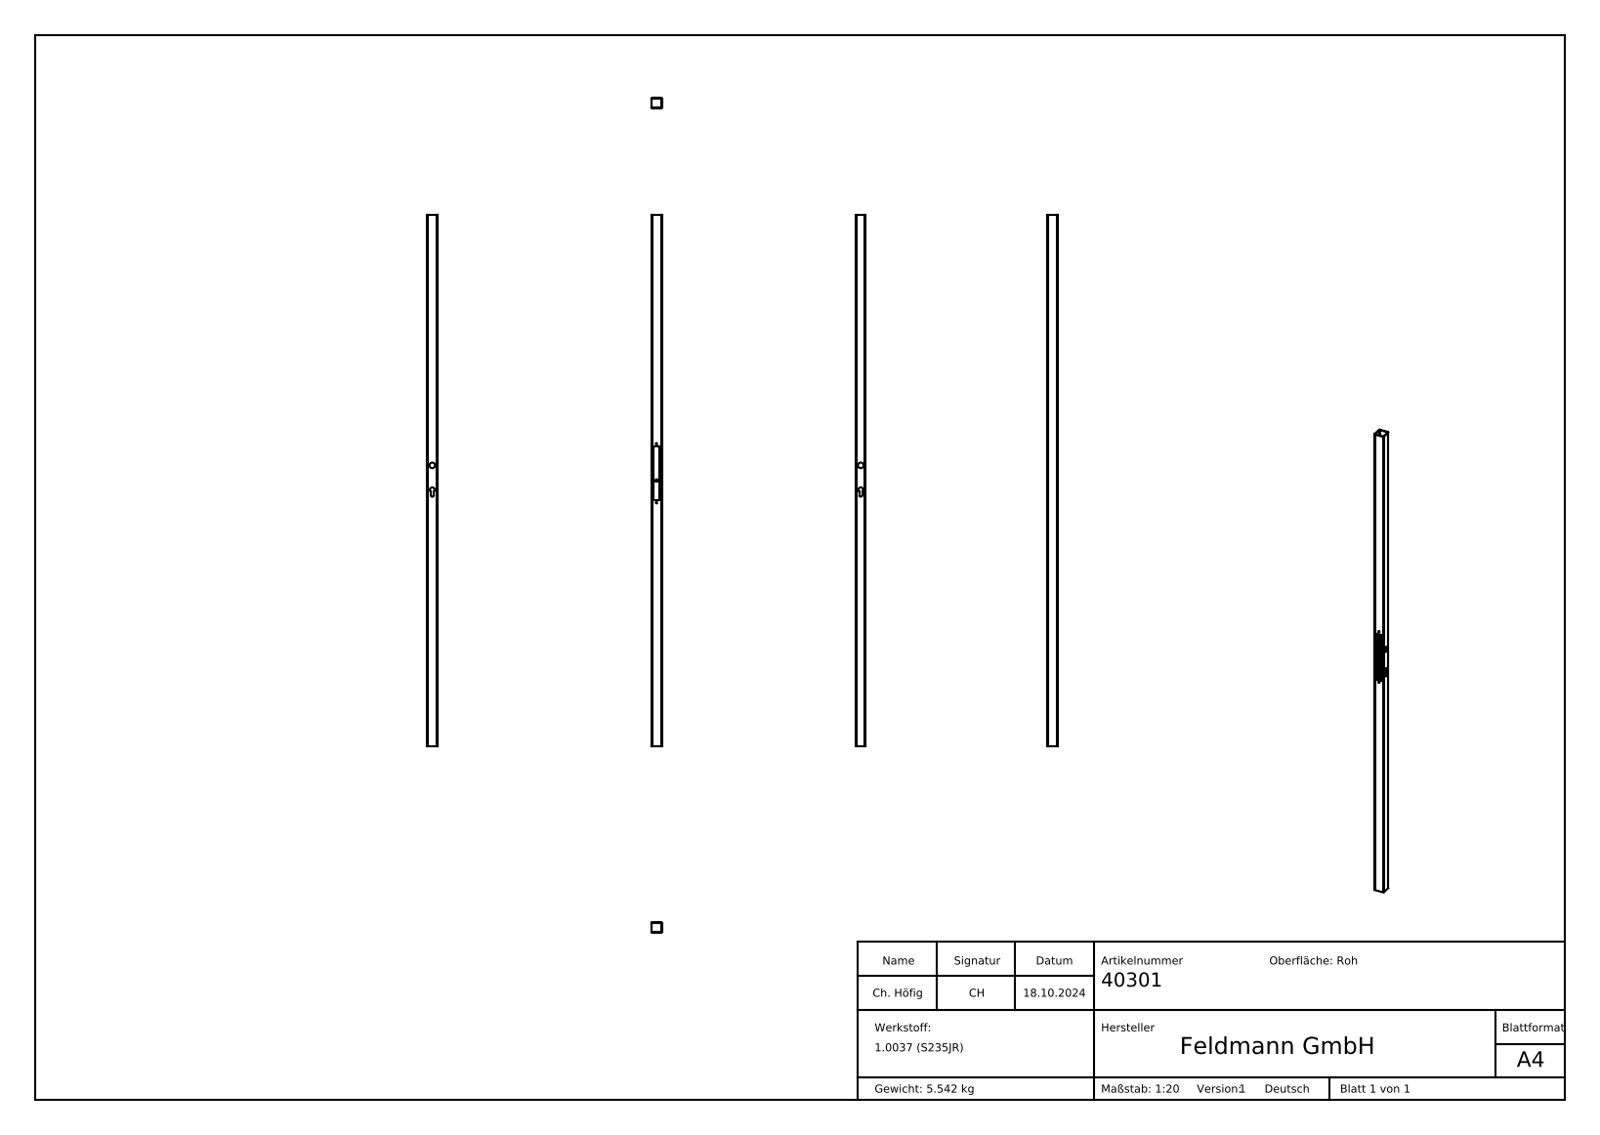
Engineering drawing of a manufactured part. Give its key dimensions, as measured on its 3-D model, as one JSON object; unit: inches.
{"part_name": "40301", "step_written_by": "SolidWorks 2018 (CONFIG_CONTROL_DESIGN)", "units": "inches", "bodies": {"solids": 1, "faces": 252, "planar": 136, "cylindrical": 16, "other": 100}, "overall_size": [78.543, 1.575, 1.575], "volume_in3": 43.36, "surface_area_in2": 885.2, "round_holes": [[0.165, 2], [0.827, 1]], "partial_cylinders_radius": [[0.059, 4], [0.157, 4], [0.222, 1], [0.36, 1]], "face_to_face_distances": [0.098, 1.476, 1.575, 1.378, 0.295, 0.394, 1.181, 1.083, 0.787, 78.543], "hole_center_spacings": [8.701]}
